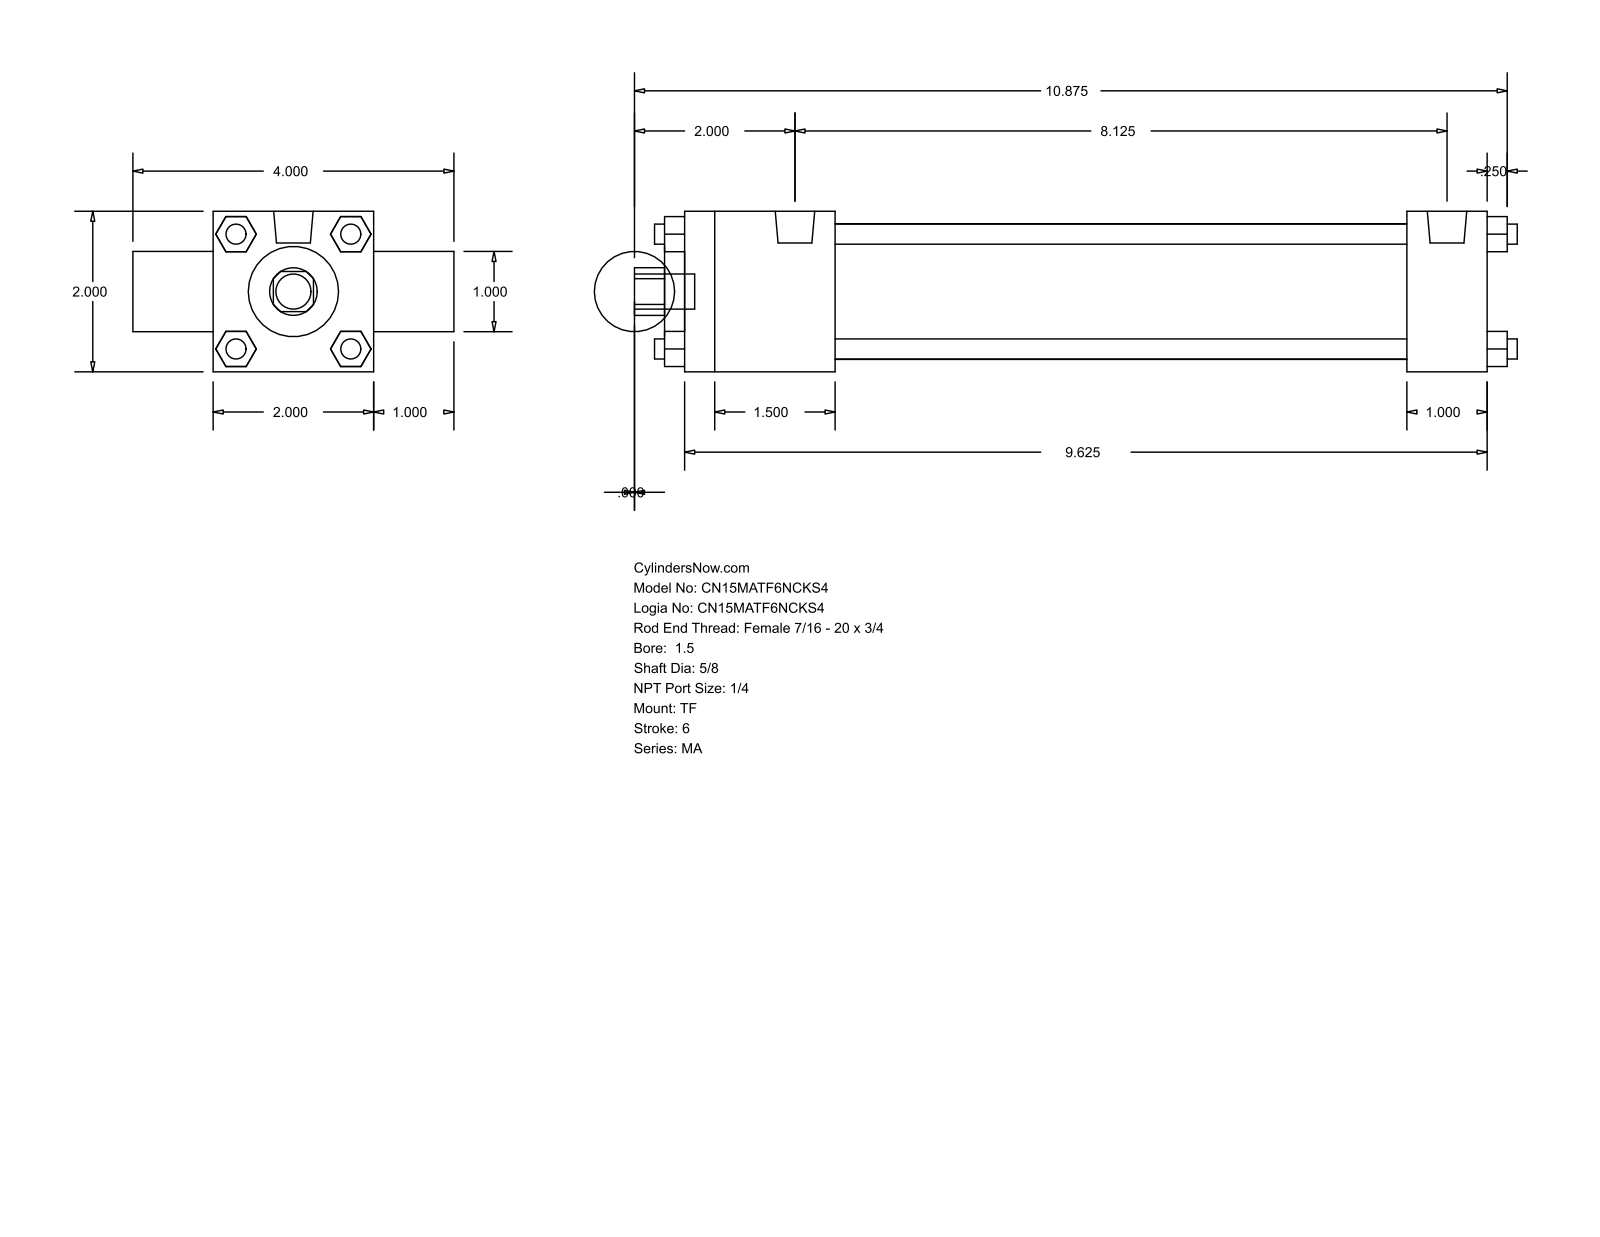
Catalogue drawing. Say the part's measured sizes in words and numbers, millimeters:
The part is named "MA_TF__0150_0.625". Its 3-D file was written by "GSSL Pune (CONFIG_CONTROL_DESIGN)". It is 0 solids with 120 faces: 92 planar, 28 cylindrical and 0 other. Overall it measures 279.4 by 101.6 by 50.8 millimeters. Round holes: 1 of diameter 15.88, 1 of diameter 25.4, 1 of diameter 28.57, 1 of diameter 42.93. Round bosses or shafts: 4 of diameter 6.35, 3 of diameter 7.94, 2 of diameter 12.49, 1 of diameter 11.11. Partial cylindrical surfaces (rounded edges, fillets, slot ends): 1 of radius 7.54. The main face-to-face distances are 50.8, 254, 260.35, 6.35, 25.4, 76.2, 47.62, 228.59, 180.97, 206.38.
